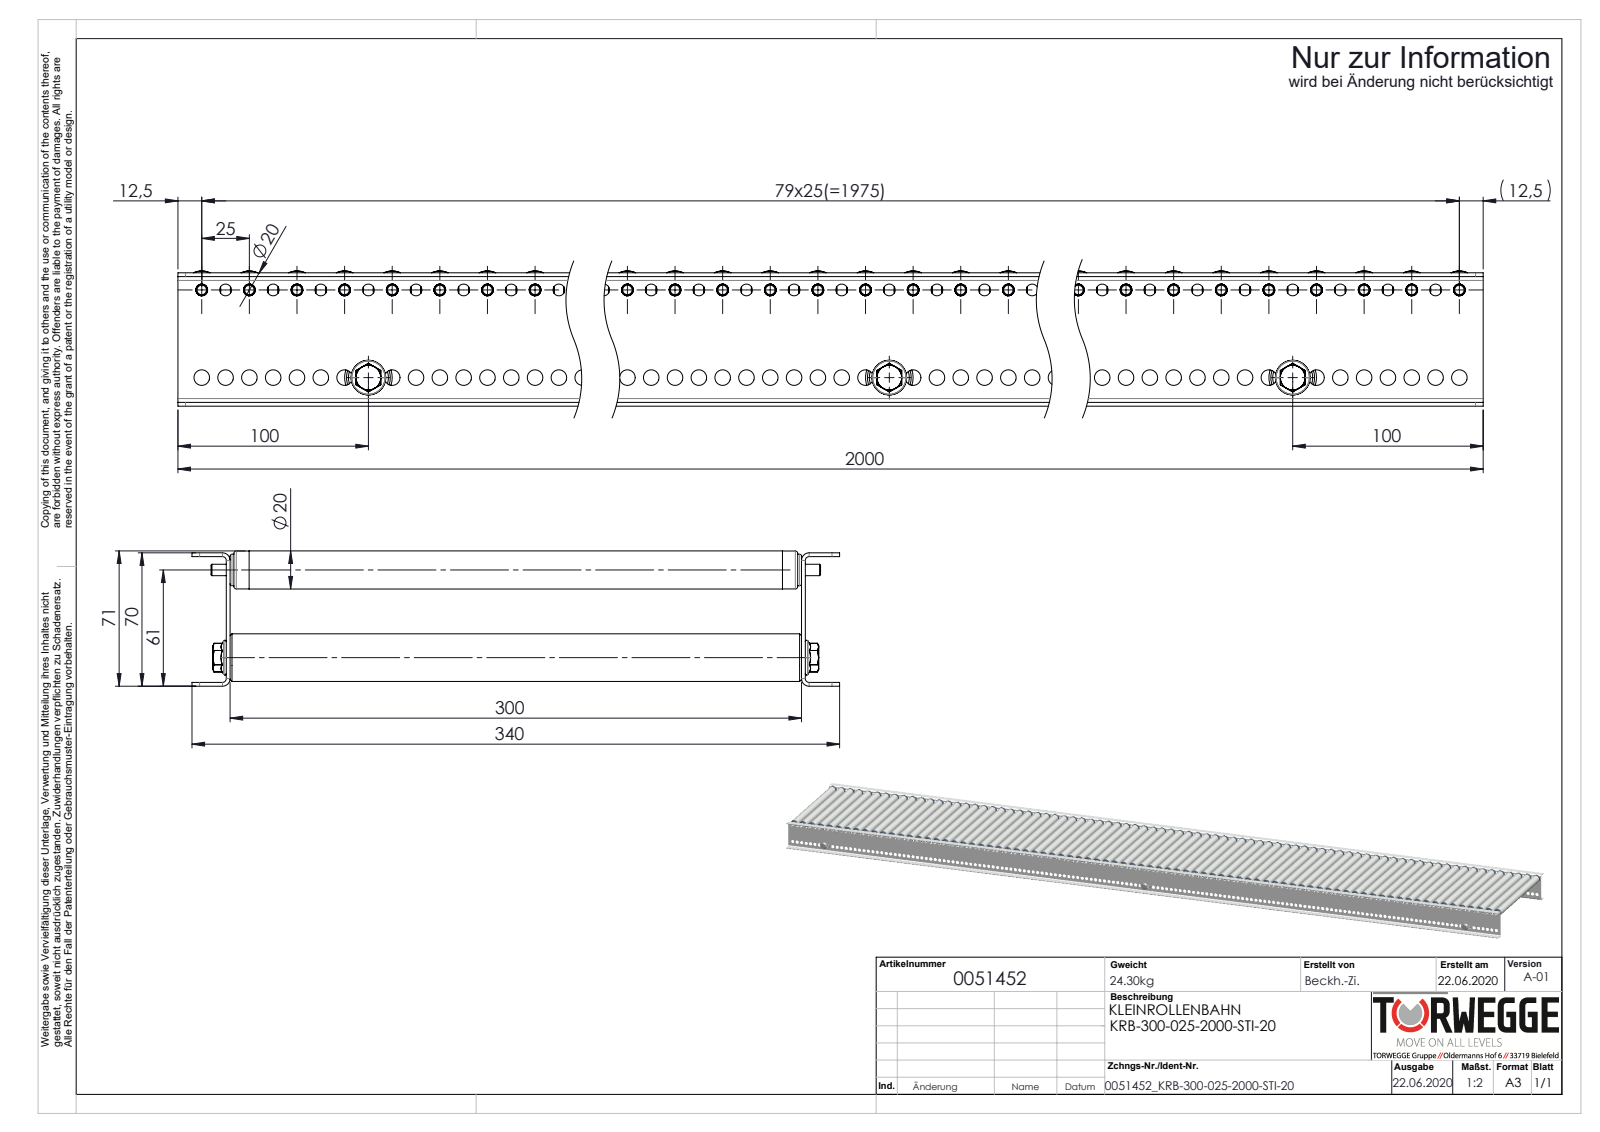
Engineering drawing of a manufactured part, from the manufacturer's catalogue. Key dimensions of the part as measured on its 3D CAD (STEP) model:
Part name (STEP PRODUCT): Profil_KRB-20x70x20x2_KFG_S100206_U-PROFIL-20-70-20-2-KRB-20-L=2000; KUT50-20x1,5-STI-A6_FA-EL=KFG_S100909_KUT50-20x1-STI-A6-FA-EL=300; S100994_Sperrzahnschraube_M08x16-8.8-A2K; 0051452 (+4 more)
STEP written by: SolidWorks 2020 (AUTOMOTIVE_DESIGN)
Units: millimetres
Bodies: 177 solids, 15746 faces (5122 planar, 5988 cylindrical, 4636 other)
Overall size (bounding box): 2000 × 340 × 71
Volume: 3 007 000 mm³ · Surface area: 4 650 000 mm²
Round holes (diameter × count): ⌀6.2 ×159, ⌀8.2 ×159, ⌀6.1 ×80, ⌀14.2 ×80, ⌀17.2 ×80, ⌀18 ×80, ⌀6.8 ×3, ⌀21 ×3
Round bosses / shafts (diameter × count): ⌀20 ×80, ⌀19.9 ×80, ⌀18.1 ×80, ⌀17.8 ×80, ⌀16.5 ×80, ⌀6 ×80, ⌀25 ×3, ⌀8 ×3
Partial cylindrical surfaces — rounded edges, fillets, slot ends (radius × count): R4.05 ×80, R4 ×8, R2 ×4
Main face-to-face distances: 2, 302, 68, 300, 304, 70, 66, 292, 18, 30
Hole centre spacings: 12.5, 25, 37.5, 50, 62.5, 75, 87.5, 100
